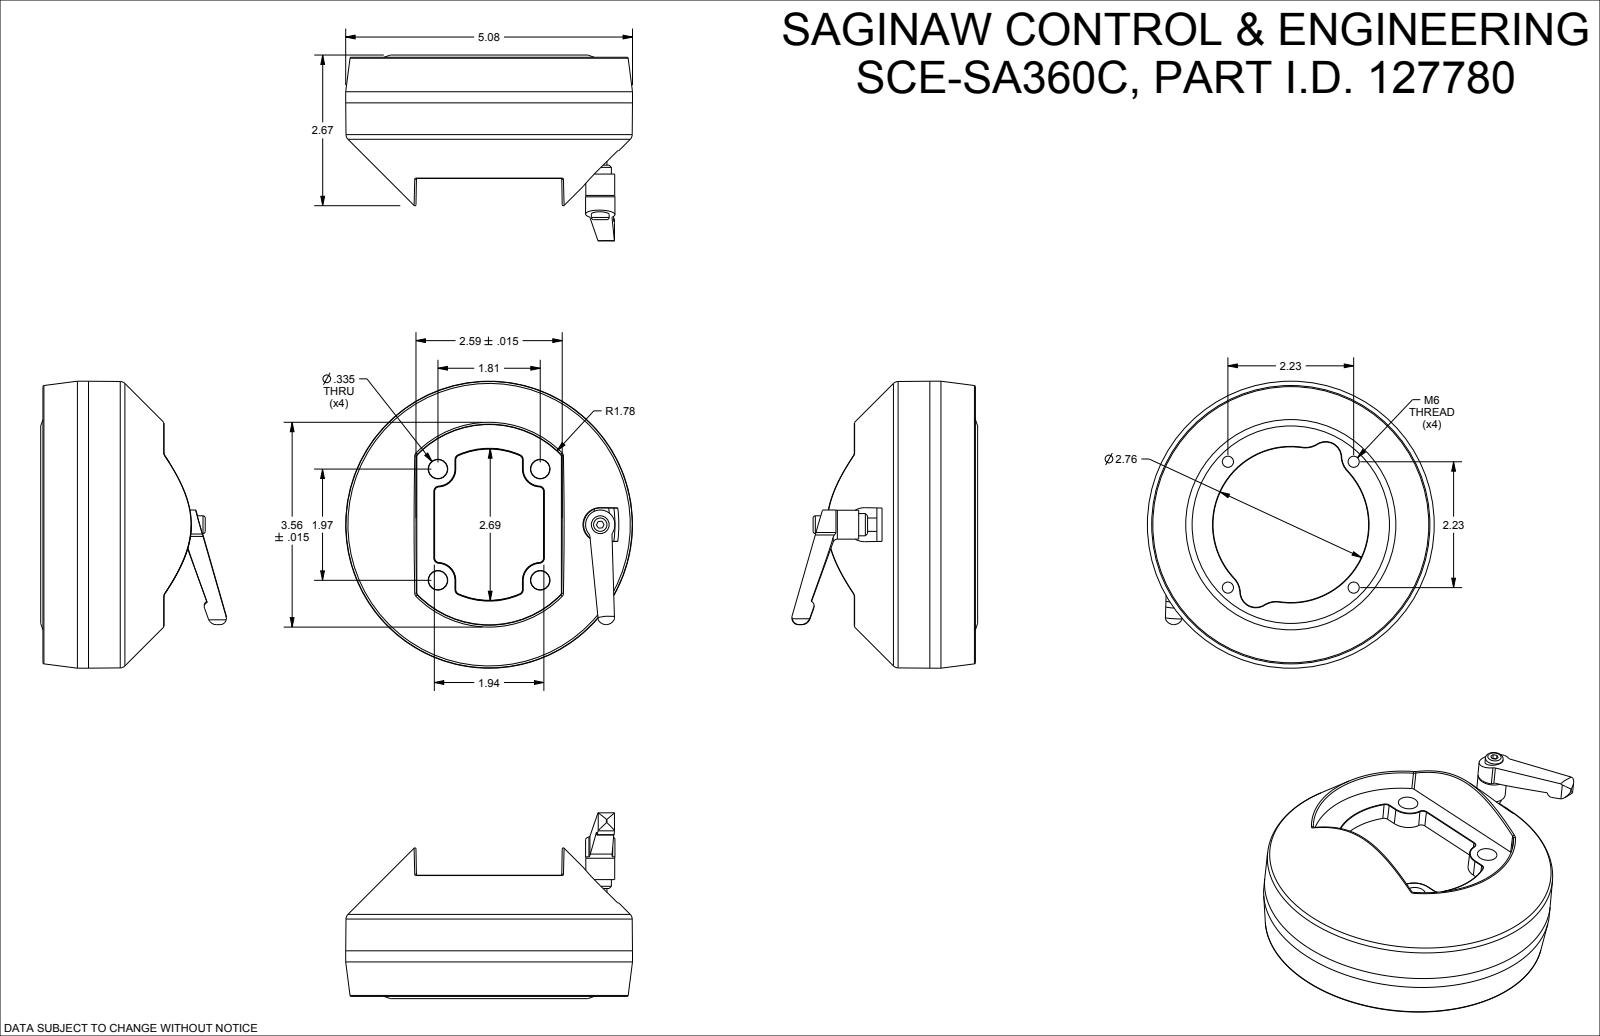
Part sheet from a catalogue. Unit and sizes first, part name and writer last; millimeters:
Units: millimetres
Overall size (bounding box): 157 × 129 × 83.5
Round holes (diameter × count): ⌀5 ×5, ⌀4.2 ×4, ⌀5.5 ×4, ⌀10 ×4, ⌀90 ×1, ⌀106 ×1
Round bosses / shafts (diameter × count): ⌀8.5 ×4, ⌀5 ×4, ⌀129 ×1, ⌀104 ×1, ⌀94.7 ×1, ⌀13 ×1, ⌀10 ×1, ⌀8 ×1
Partial cylindrical surfaces — rounded edges, fillets, slot ends (radius × count): R0.2 ×12, R1 ×7, R2 ×5, R10 ×4, R7 ×2, R4 ×1, R6.6 ×1, R35 ×1
Main face-to-face distances: 20.5, 18, 2.5, 1, 19, 21.5, 38.5, 39.5, 8, 46.5
Hole centre spacings: 38.8, 40, 41.1, 56.5, 56.6, 79.9, 88.8, 89.9
Volume: 350 200 mm³ · Surface area: 105 200 mm²
Bodies: 5 solids, 446 faces (115 planar, 78 cylindrical, 253 other)
Part name (STEP PRODUCT): SCE-SA360C
STEP written by: SolidWorks 2023 (AUTOMOTIVE_DESIGN)
